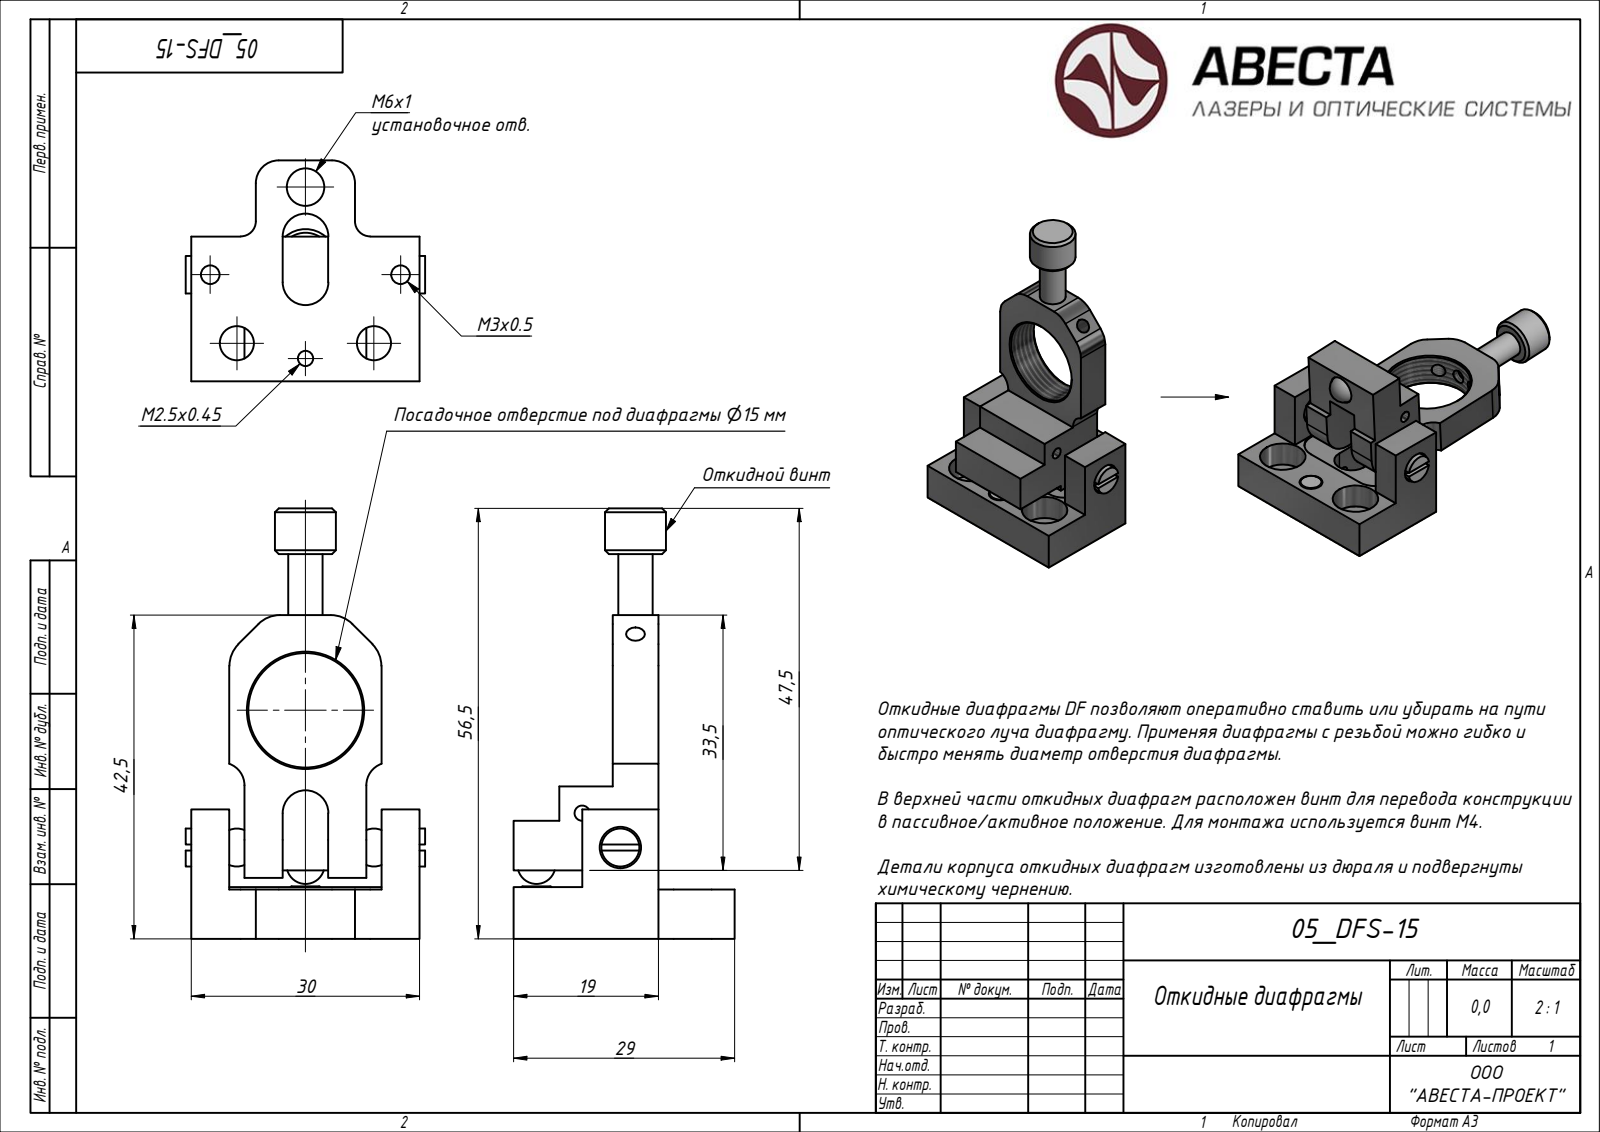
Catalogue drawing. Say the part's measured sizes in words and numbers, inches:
The part is named "05_DFS-15; M01_Основание; M02_Откидушка; Пятка4х4 (+4 more)". Its 3-D file was written by "Autodesk Inventor 2020 (CONFIG_CONTROL_DESIGN)". It is 11 solids with 150 faces: 69 planar, 54 cylindrical and 27 other. Overall it measures 2.224 by 1.239 by 1.142 inches. Its volume is 0.521 cubic inches and its surface area 11.86 square inches. Round holes: 5 of diameter 0.097, 2 of diameter 0.079, 2 of diameter 0.177, 2 of diameter 0.315, 1 of diameter 0.079, 1 of diameter 0.118, 1 of diameter 0.157, 1 of diameter 0.194, 1 of diameter 0.197, 1 of diameter 0.215, 1 of diameter 0.591. Round bosses or shafts: 1 of diameter 0.315, 1 of diameter 0.236, 1 of diameter 0.197, 1 of diameter 0.177, 1 of diameter 0.118. Partial cylindrical surfaces (rounded edges, fillets, slot ends): 7 of radius 0.118, 6 of radius 0.157, 2 of radius 0.079, 1 of radius 0.197. The main face-to-face distances are 0.276, 0.512, 0.197, 0.709, 0.236, 0.079, 0.433, 0.354, 0.906, 0.472. The hole center spacings are 0.363, 0.38, 0.498, 0.559, 0.656, 0.669, 0.881, 0.918.
